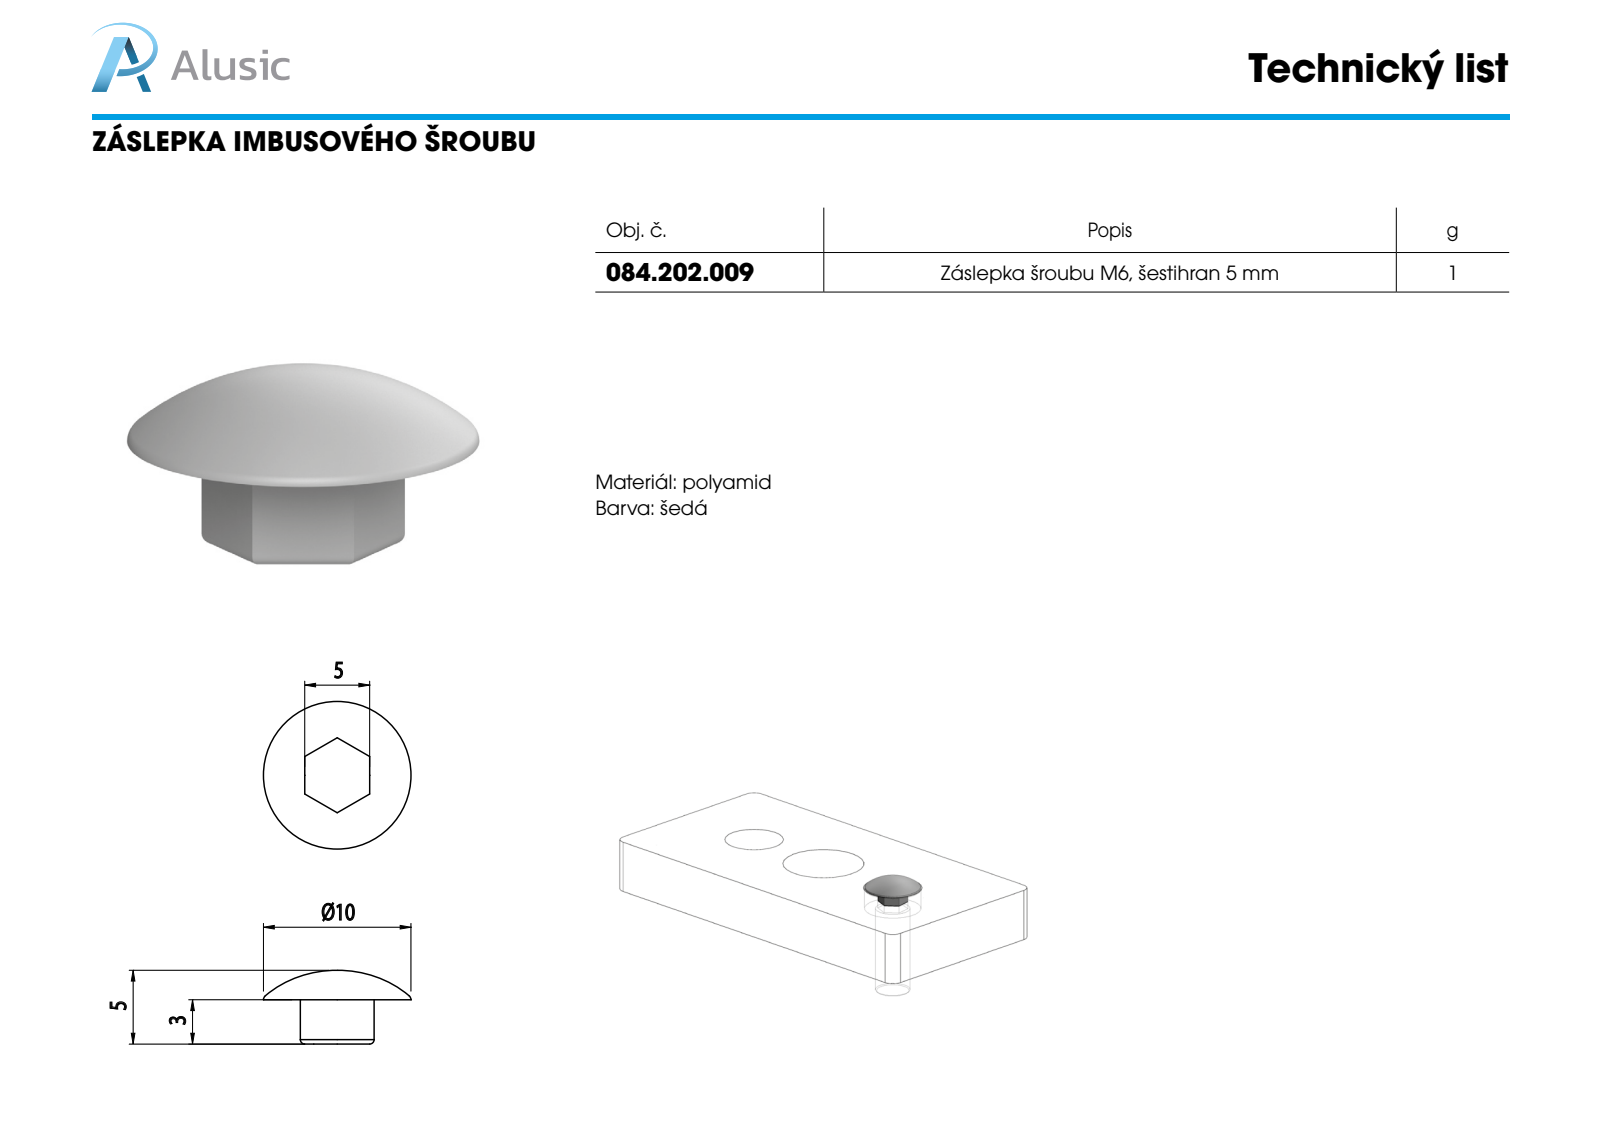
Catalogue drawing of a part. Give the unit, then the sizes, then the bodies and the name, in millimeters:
Units: millimetres
Overall size (bounding box): 10 × 10 × 5
Partial cylindrical surfaces — rounded edges, fillets, slot ends (radius × count): R0.3 ×18
Main face-to-face distances: 1, 4, 5, 3
Volume: 129 mm³ · Surface area: 250 mm²
Bodies: 1 solid, 37 faces (15 planar, 18 cylindrical, 4 other)
Part name (STEP PRODUCT): 084.202.009
STEP written by: SolidWorks 2011 (CONFIG_CONTROL_DESIGN)
